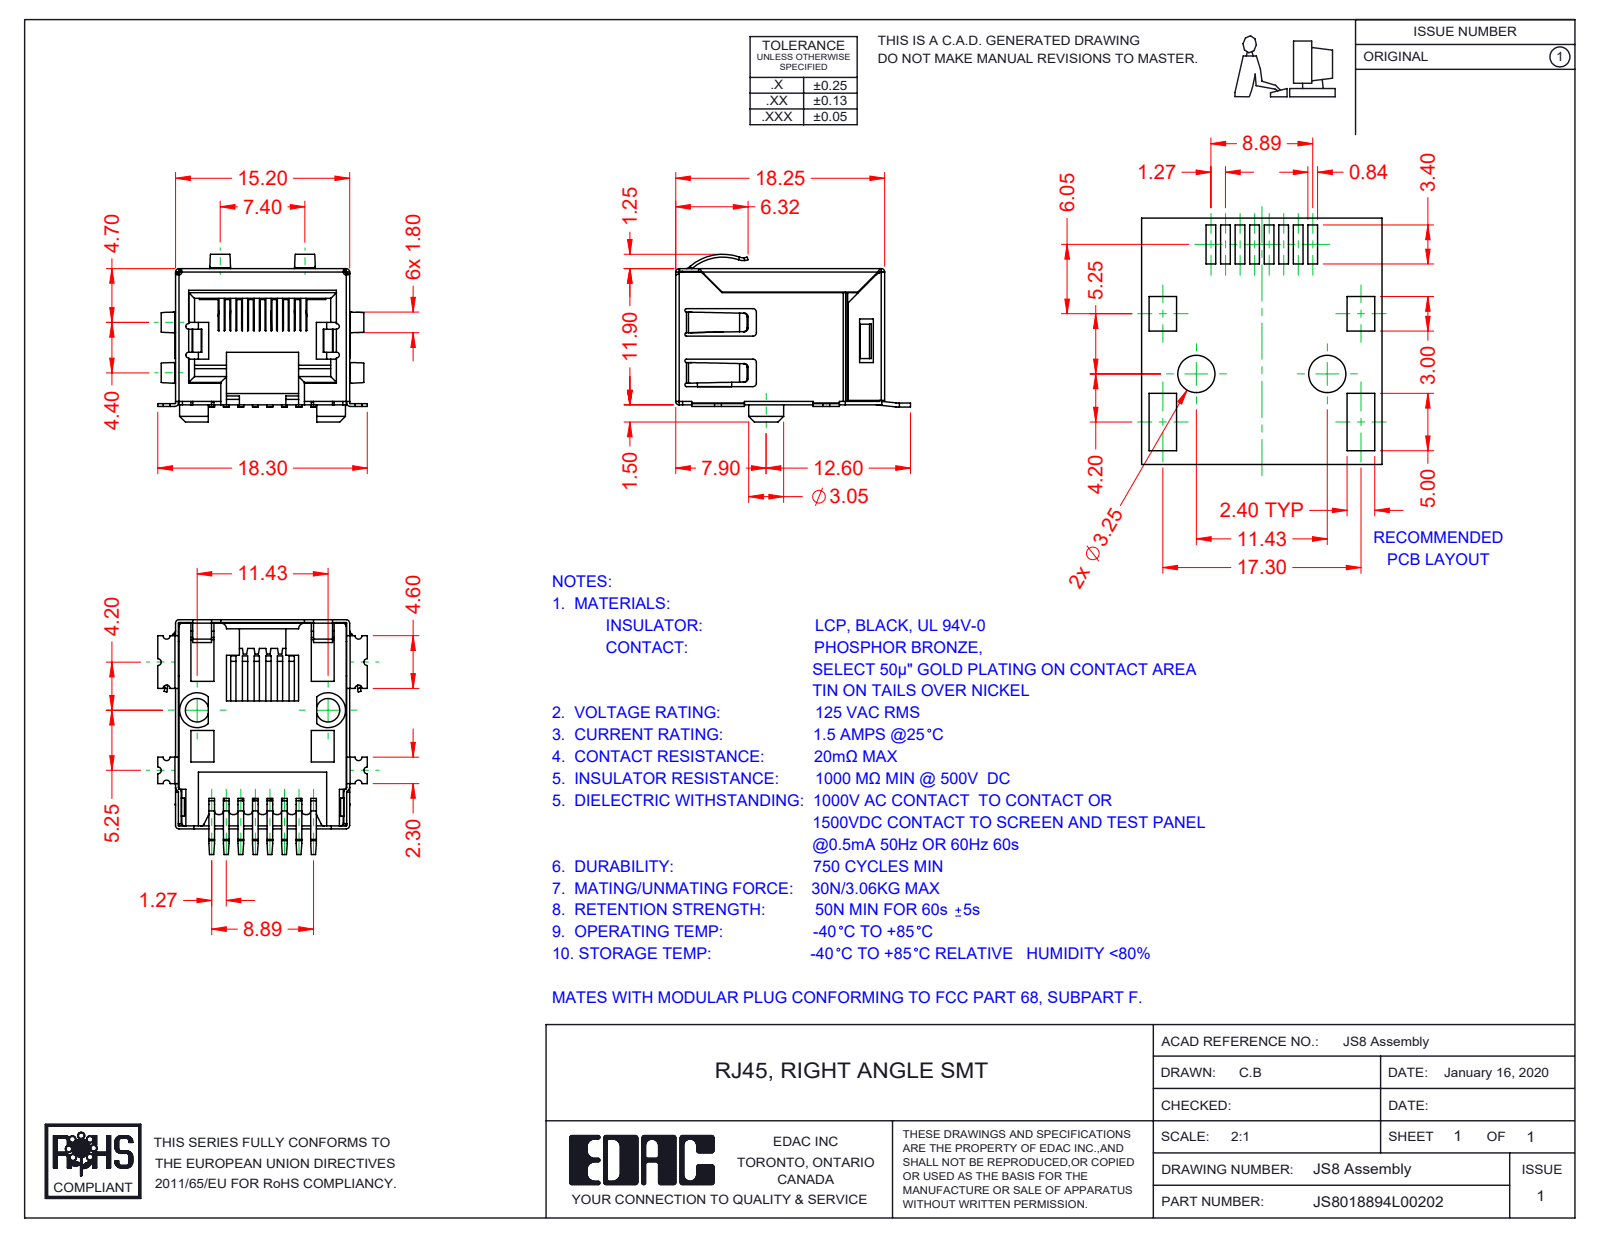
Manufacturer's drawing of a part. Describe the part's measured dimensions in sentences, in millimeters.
The part is named "RJS8018894L00202; S8 Shield; S8 Insulator; S8 Contacts". Its 3-D file was written by "SolidWorks 2016 (CONFIG_CONTROL_DESIGN)". It is 10 solids with 976 faces: 602 planar, 314 cylindrical and 60 other. Overall it measures 20.5 by 18.3 by 14.65 millimeters. Its volume is 1 308 cubic millimeters and its surface area 4 634 square millimeters. Partial cylindrical surfaces (rounded edges, fillets, slot ends): 59 of radius 0.3, 19 of radius 0.25, 18 of radius 0.5, 17 of radius 0.2, 8 of radius 0.15, 7 of radius 0.75, 4 of radius 1, 3 of radius 1.25. The main face-to-face distances are 14.65, 14.95, 14.9, 1, 0.35, 14.7, 0.75, 10.9, 1.1, 15.2.
